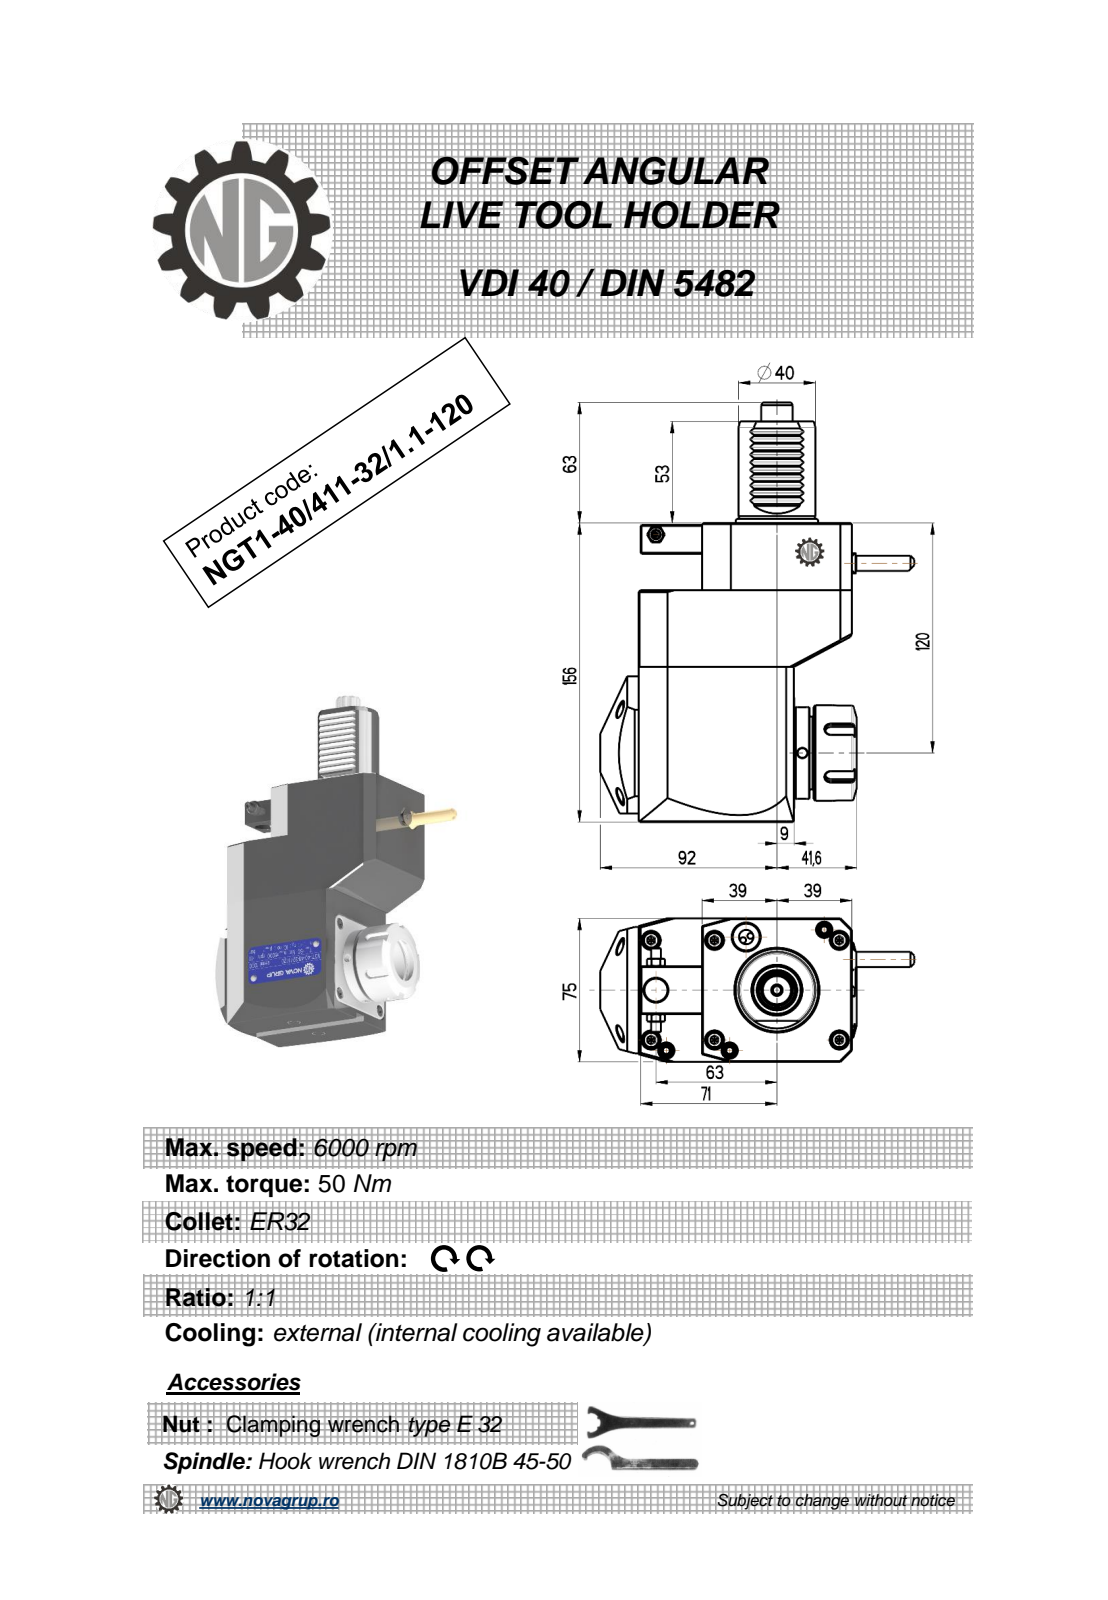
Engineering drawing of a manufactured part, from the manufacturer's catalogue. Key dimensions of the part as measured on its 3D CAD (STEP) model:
Part name (STEP PRODUCT): NGT1_40_411_32_1_1_120
STEP written by: PRO/ENGINEER BY PARAMETRIC TECHNOLOGY CORPORATION, 2010280 (CONFIG_CONTROL_DESIGN)
Units: millimetres
Bodies: 1 solid, 469 faces (201 planar, 124 cylindrical, 144 other)
Overall size (bounding box): 219 × 163.5 × 76.6
Volume: 1 180 000 mm³ · Surface area: 87 059 mm²
Round holes (diameter × count): ⌀5 ×3, ⌀4.2 ×2, ⌀3 ×1, ⌀9.5 ×1, ⌀12 ×1, ⌀27 ×1
Round bosses / shafts (diameter × count): ⌀50 ×1, ⌀48 ×1, ⌀41 ×1, ⌀40 ×1, ⌀11.2 ×1, ⌀8.96 ×1, ⌀8 ×1, ⌀5 ×1
Partial cylindrical surfaces — rounded edges, fillets, slot ends (radius × count): R3.03 ×18, R0.26 ×12, R0.3 ×10, R0.22 ×6, R3 ×5, R0.5 ×1, R6.75 ×1, R8.22 ×1
Main face-to-face distances: 75, 156, 111, 35, 121, 30, 81, 33, 48, 78
Hole centre spacings: 13.25, 20.93, 63, 76.25, 100.28, 112.5, 137.15
